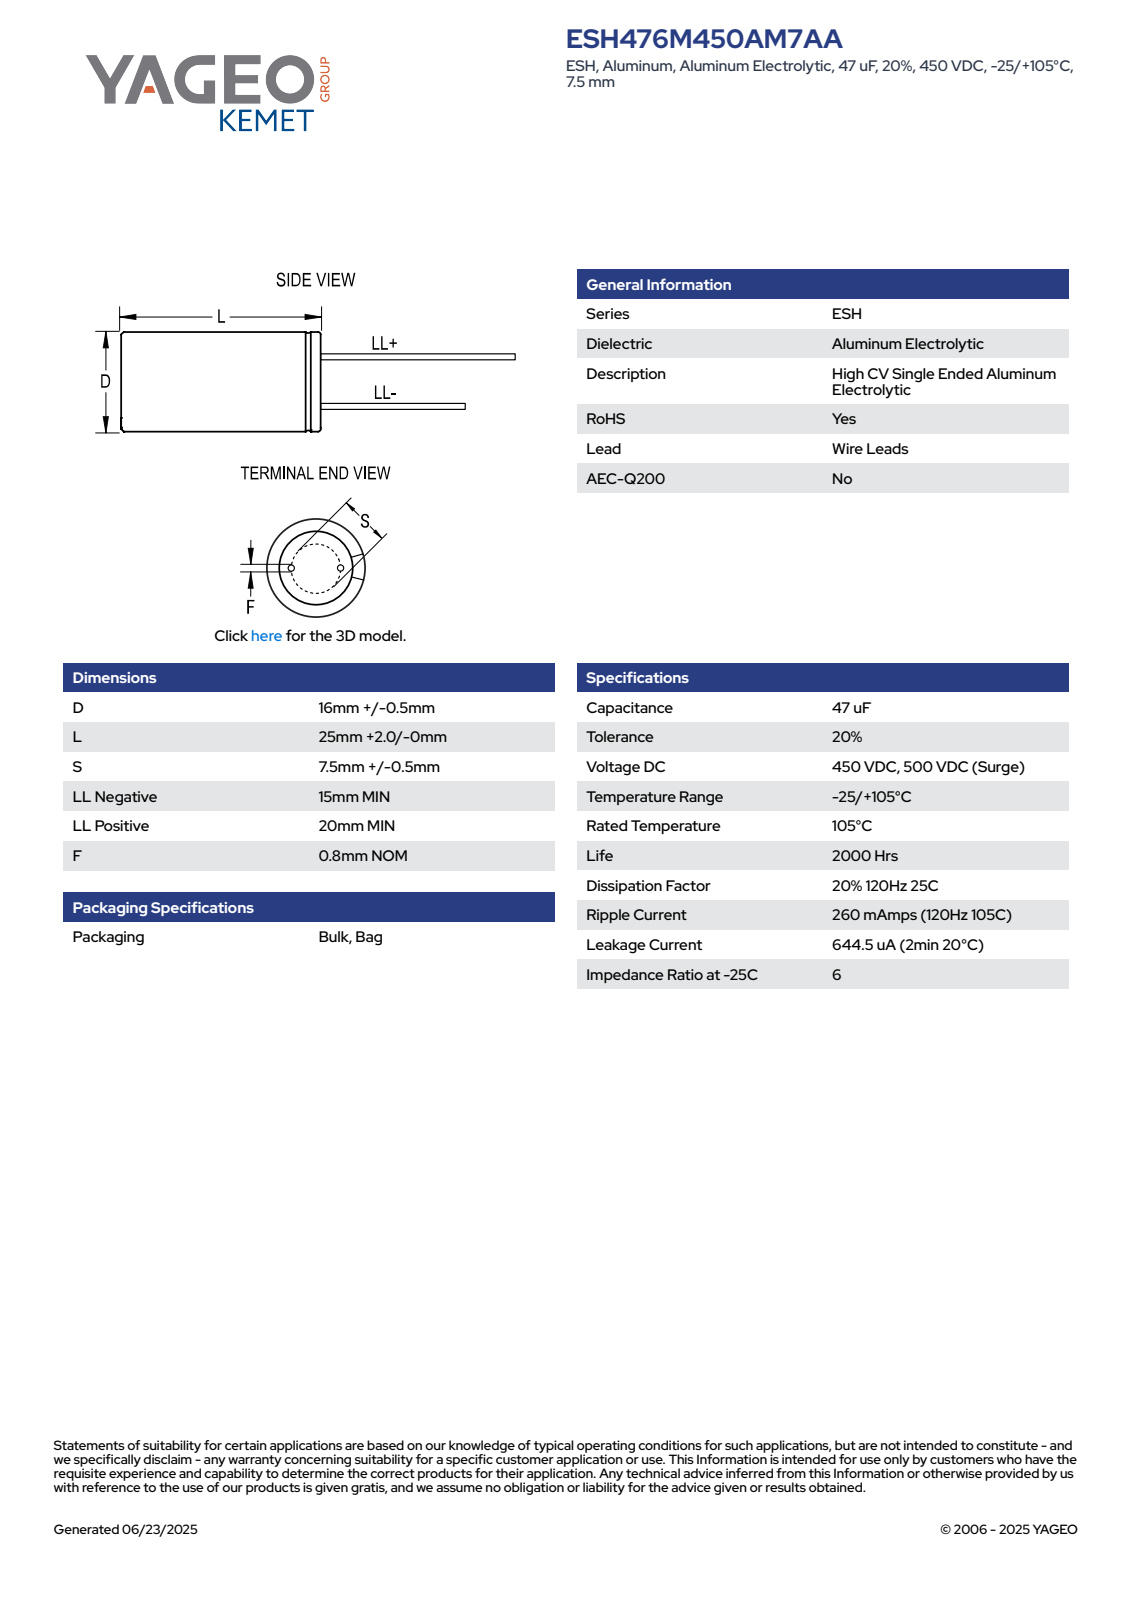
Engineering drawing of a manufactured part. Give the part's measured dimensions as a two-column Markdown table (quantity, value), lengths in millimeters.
| quantity | value |
| --- | --- |
| part name | CAR_KLP_16X25_D16.5L27S7.5F0.8 |
| STEP written by | SolidWorks 2014 (AUTOMOTIVE_DESIGN) |
| units | millimeters |
| bodies | 4 solids, 75 faces (61 planar, 8 cylindrical, 6 other) |
| overall size | 47.01 × 16.5 × 16.5 |
| volume | 5 744 mm³ |
| surface area | 1 978 mm² |
| round bosses / shafts (diameter × count) | 0.8 × 2, 16.5 × 1 |
| main face-to-face distances | 27, 27.01, 5, 42.01, 47.01, 42, 47, 15, 20, 2.22 |
